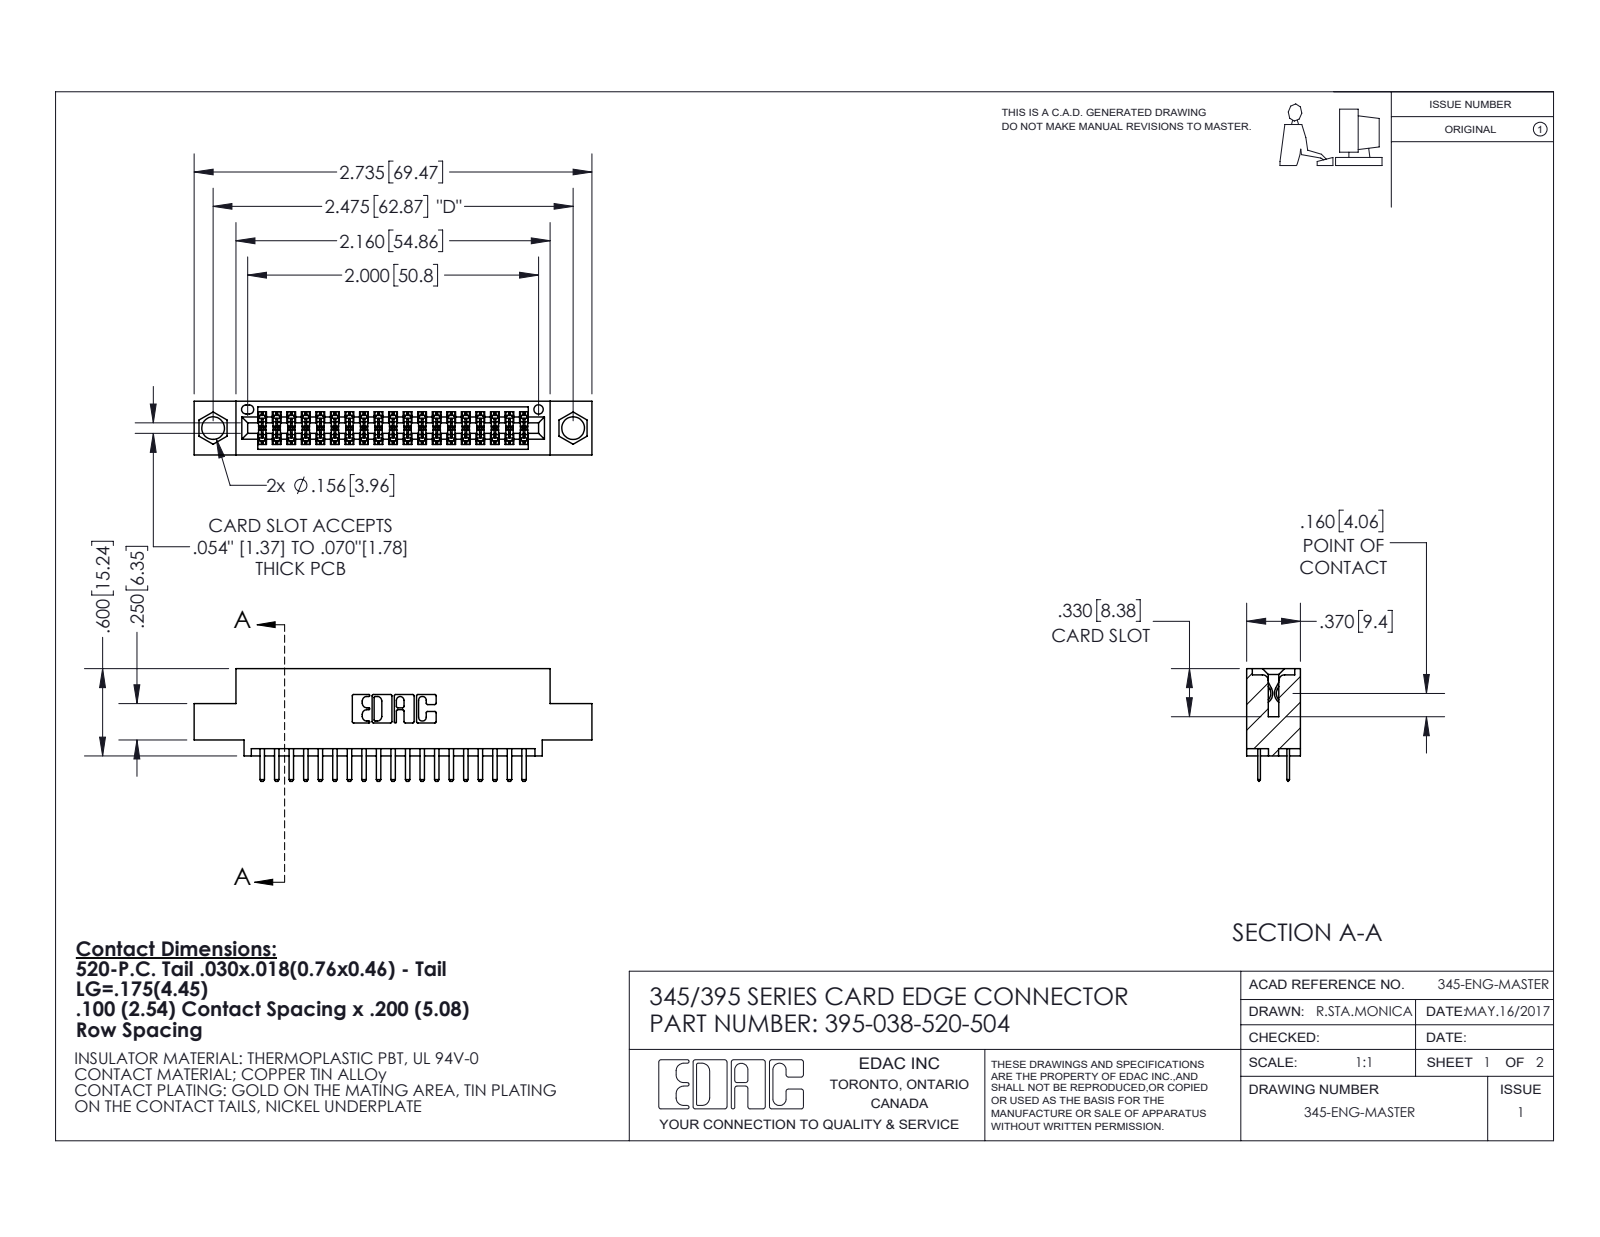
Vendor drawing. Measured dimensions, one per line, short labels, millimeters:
name: 395-038-520-504; 345 Part_0.110 Offset - 0.156 Dia-TI; 345-292-001_345-293-120
written by: SolidWorks 2020 (CONFIG_CONTROL_DESIGN)
unit: mm
bodies: 39 solids, 2196 faces (1428 planar, 768 cylindrical, 0 other)
size: 69.5 × 19.7 × 9.4
volume: 6 340 mm³; area: 8 832 mm²
holes: 2× ⌀4, 1× ⌀1.6
rounds: 57× R0.2, 42× R0.3, 22× R0.3, 6× R0.2, 6× R0.8, 3× R0.7, 2× R0.4, 2× R0.5
face distances: 1.8, 7.6, 5.1, 9.4, 2.5, 6.9, 0.6, 5.7, 0.6, 1.8
hole spacings: 6.9, 56.9, 62.9
